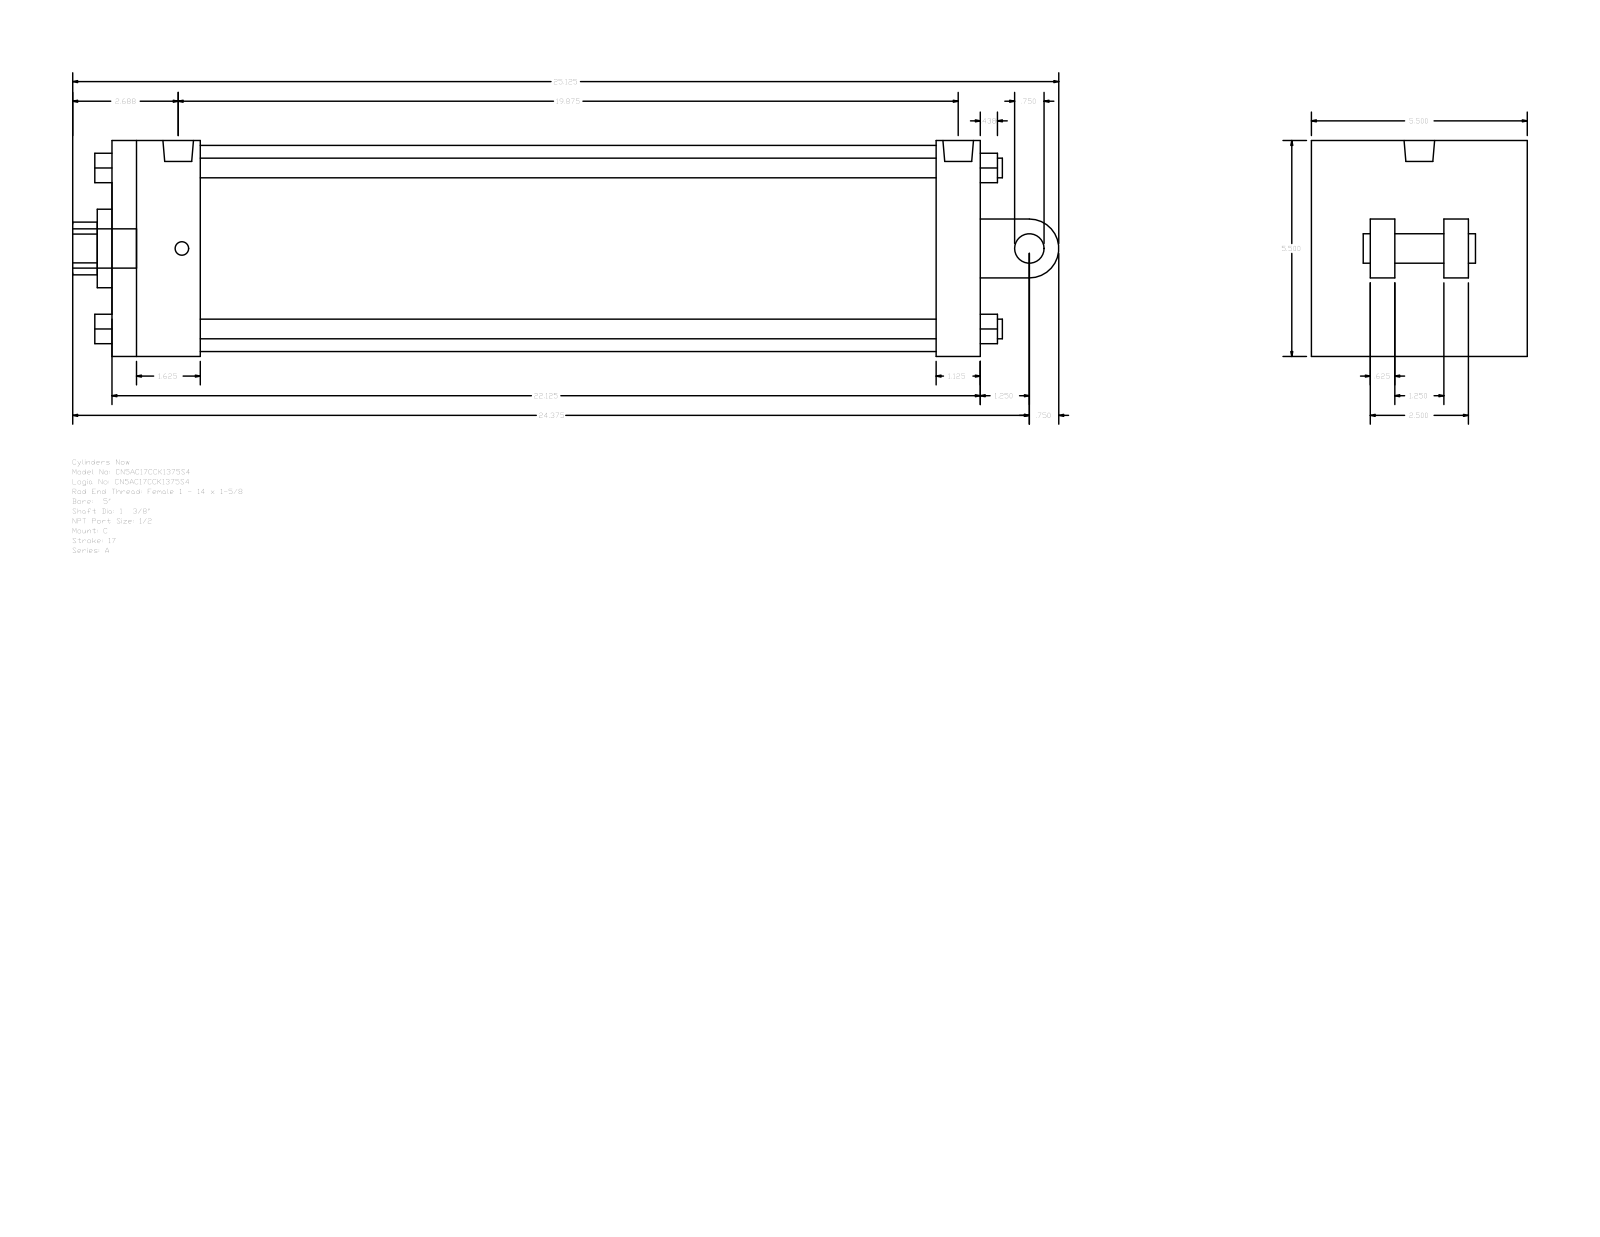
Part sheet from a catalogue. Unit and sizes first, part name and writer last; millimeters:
Units: millimetres
Overall size (bounding box): 638.17 × 139.7 × 139.7
Round holes (diameter × count): ⌀8.73 ×2, ⌀19.77 ×1, ⌀34.92 ×1, ⌀50.8 ×1, ⌀133.35 ×1
Round bosses / shafts (diameter × count): ⌀12.7 ×4, ⌀8.73 ×2, ⌀25.4 ×1, ⌀19.77 ×1, ⌀19.05 ×1
Partial cylindrical surfaces — rounded edges, fillets, slot ends (radius × count): R17.06 ×1, R19.05 ×1
Main face-to-face distances: 139.7, 561.98, 28.58, 57.15, 533.4, 476.25, 504.83, 38.1, 15.87, 53.97
Hole centre spacings: 2.39
Bodies: 0 solids, 135 faces (102 planar, 33 cylindrical, 0 other)
Part name (STEP PRODUCT): A_C__0500_1.375
STEP written by: GSSL Pune (CONFIG_CONTROL_DESIGN)
